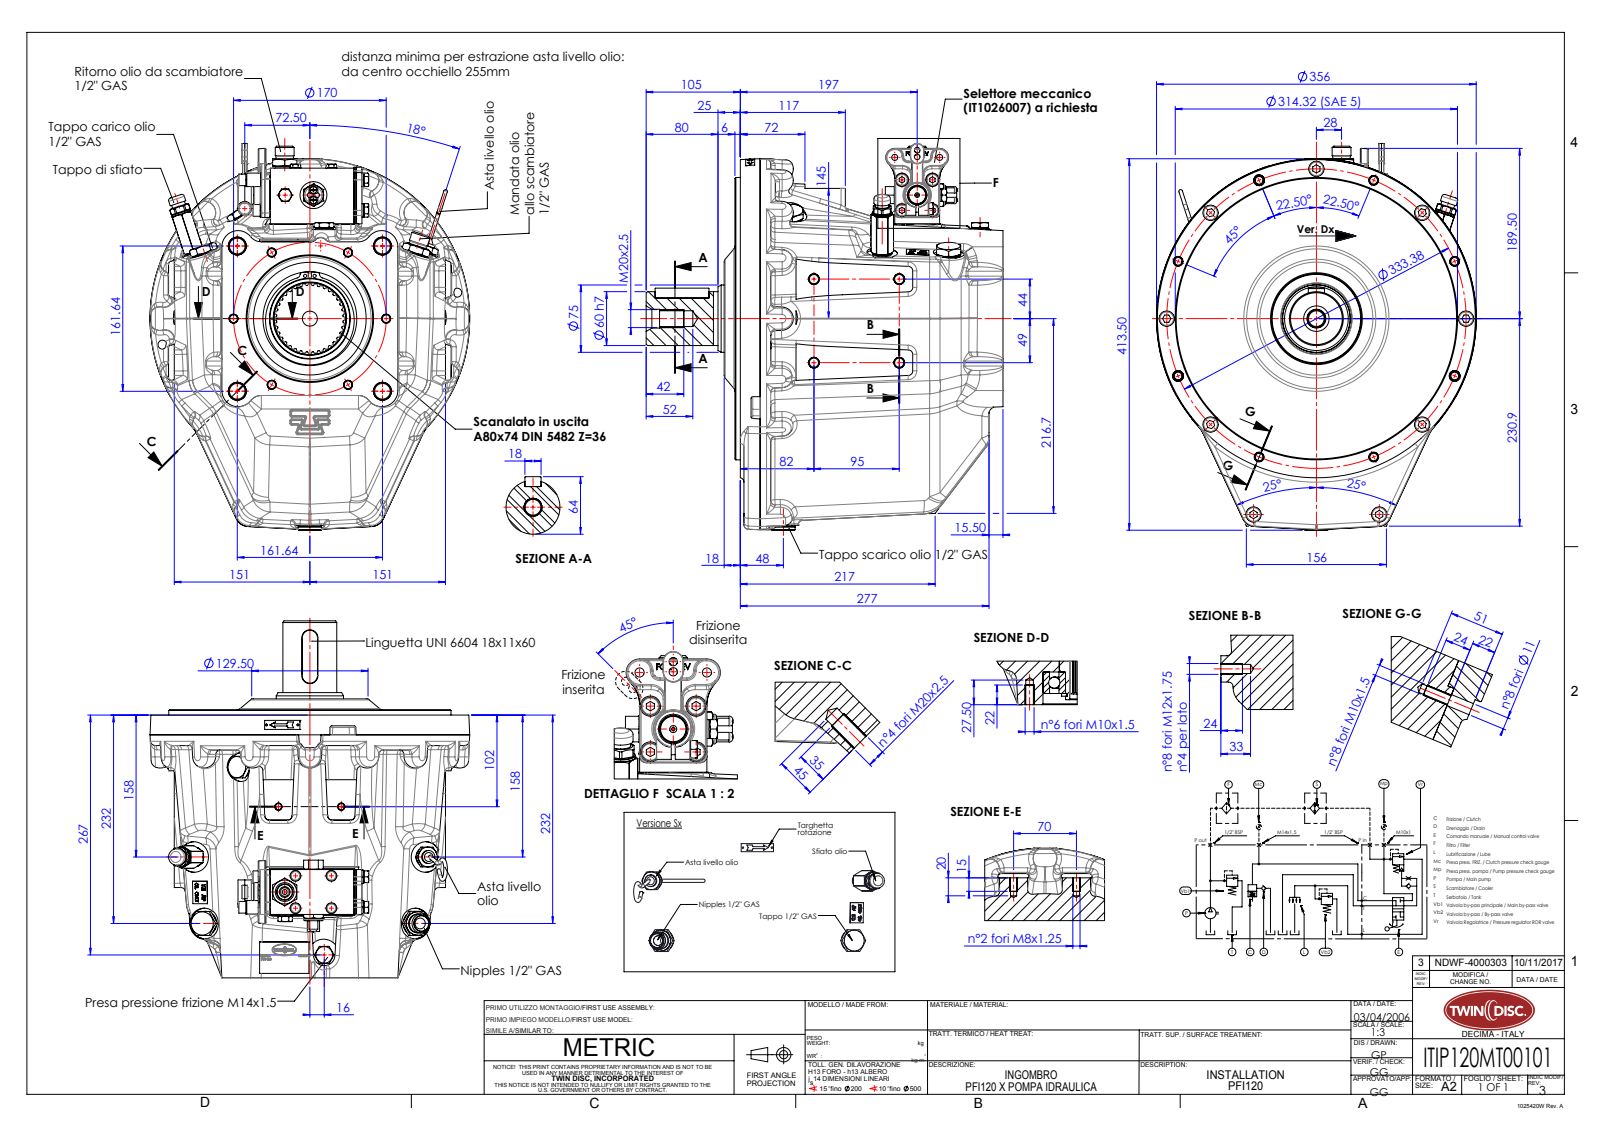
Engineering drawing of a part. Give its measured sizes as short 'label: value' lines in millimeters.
name: ITIP120MT00101
written by: SolidWorks 2015 (AUTOMOTIVE_DESIGN)
unit: mm
bodies: 0 solids, 2142 faces (657 planar, 570 cylindrical, 915 other)
size: 430.5 × 397.4 × 356
holes: 9× ⌀17, 8× ⌀11, 6× ⌀8.5, 5× ⌀6.8, 5× ⌀17.5, 4× ⌀10.2, 4× ⌀34, 3× ⌀12, 2× ⌀3.5, 2× ⌀6.2, 2× ⌀10, 1× ⌀2
bosses: 6× ⌀15, 4× ⌀14.8, 4× ⌀13, 4× ⌀12, 3× ⌀22, 3× ⌀20, 3× ⌀4, 2× ⌀27
rounds: 92× R5, 66× R0.35, 45× R1, 26× R22, 18× R3, 14× R28, 11× R10, 8× R18
face distances: 28, 22, 6, 18, 270.5, 292.5, 298.5, 10, 40, 4
hole spacings: 166.69, 85, 65.04, 127.58, 202.11, 75.14, 117.92, 147.22
